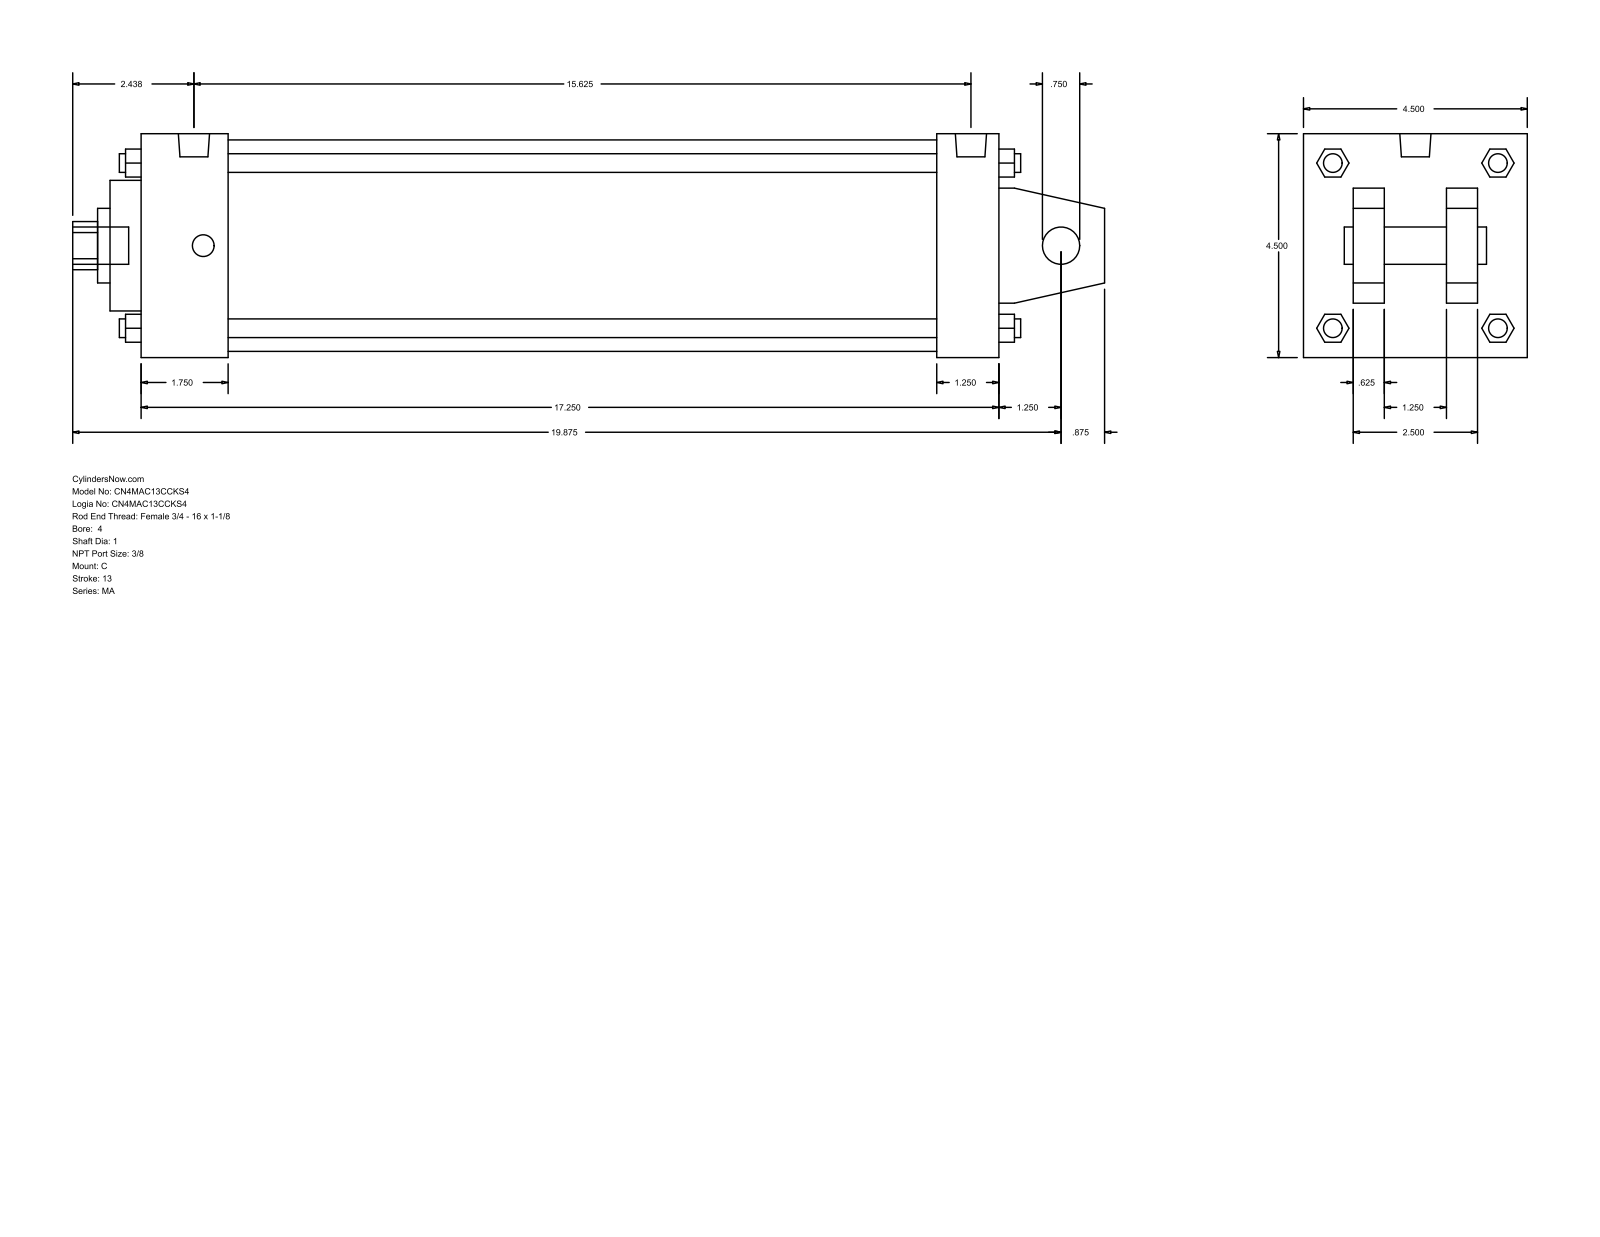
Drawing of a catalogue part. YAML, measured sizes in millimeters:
part_name: "MA_C__0400_1"
step_written_by: "GSSL Pune (CONFIG_CONTROL_DESIGN)"
units: millimeters
bodies: {solids: 0, faces: 141, planar: 109, cylindrical: 32, other: 0}
overall_size: [527.05, 114.3, 114.3]
round_holes:
  - {diameter: 19.05, count: 1}
  - {diameter: 25.4, count: 1}
  - {diameter: 38.1, count: 1}
  - {diameter: 66.67, count: 1}
  - {diameter: 107.95, count: 1}
round_bosses_or_shafts:
  - {diameter: 11.11, count: 4}
  - {diameter: 9.53, count: 4}
  - {diameter: 15.93, count: 2}
  - {diameter: 19.05, count: 1}
partial_cylinders:
  - {radius: 12.29, count: 1}
face_to_face_distances: [114.3, 438.15, 15.87, 73.03, 41.27, 25.4, 88.9, 47.63, 406.4, 31.75]
